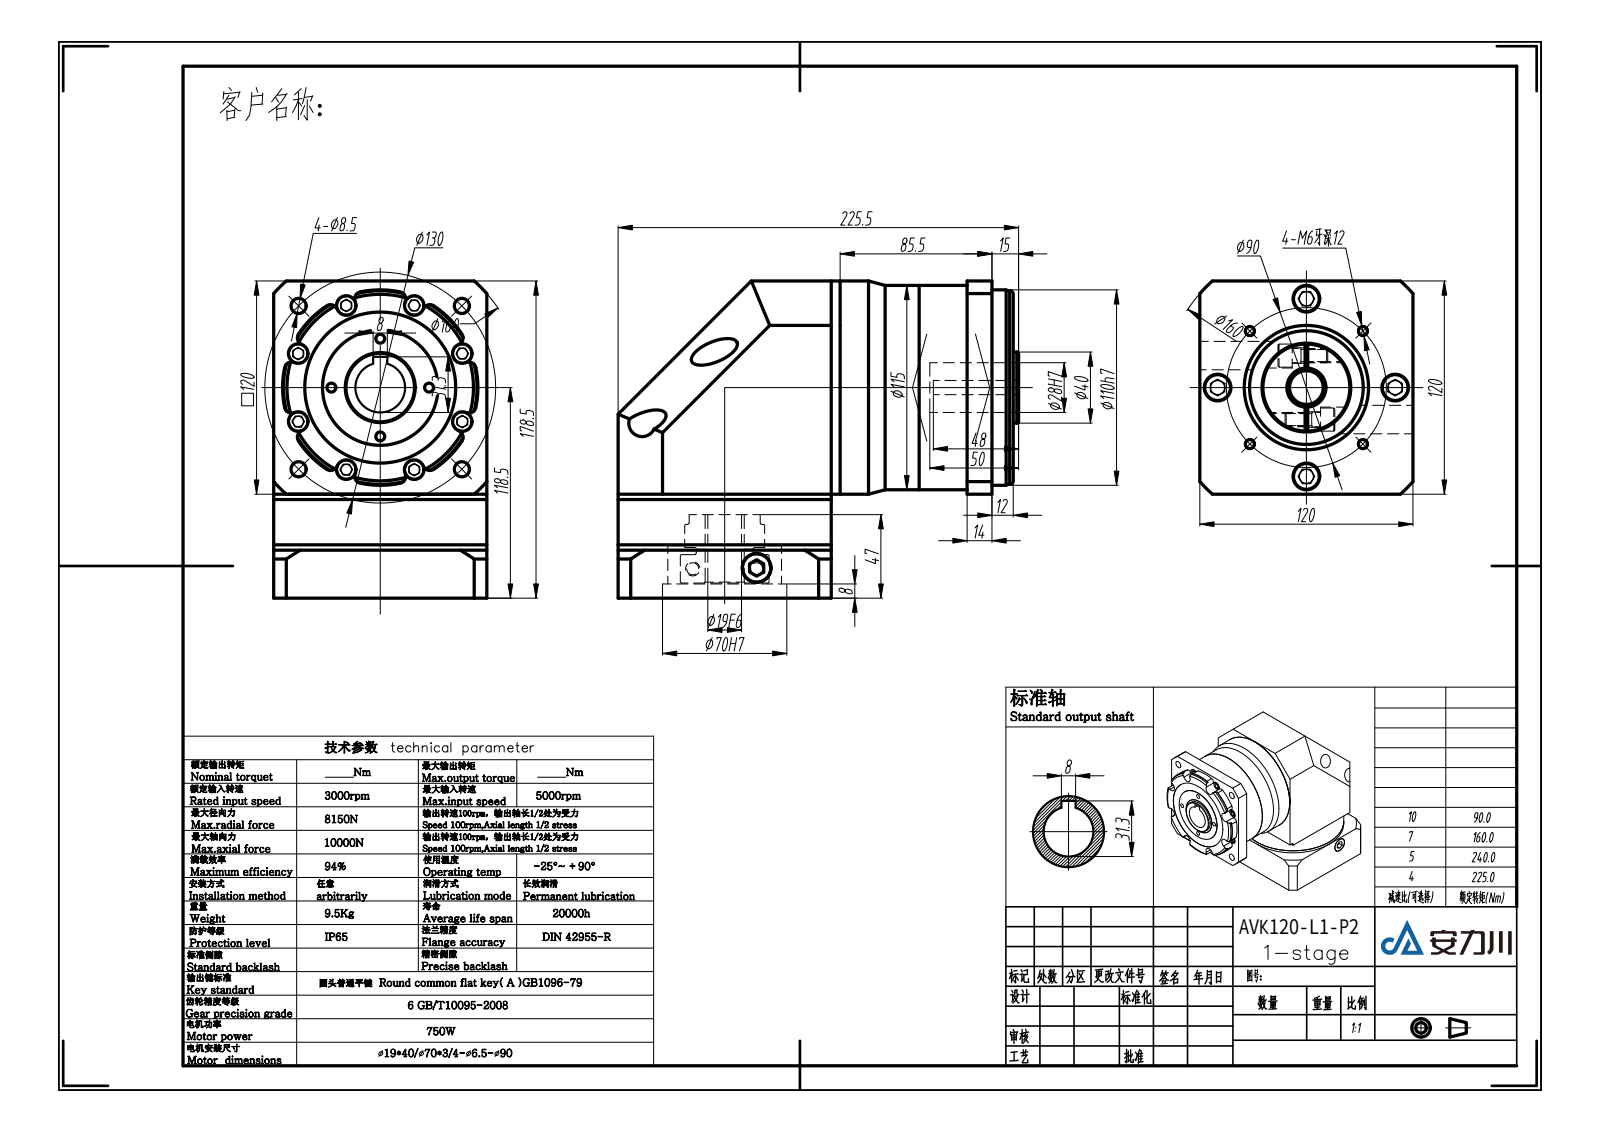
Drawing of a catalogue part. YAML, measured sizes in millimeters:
part_name: "VGZK115单级模型（19-40 70-3 4-6.5-90）"
step_written_by: "SolidWorks 2016 (AUTOMOTIVE_DESIGN)"
units: millimeters
bodies: {solids: 23, faces: 501, planar: 278, cylindrical: 198, other: 25}
overall_size: [225.5, 178.5, 120]
volume: 2959000
surface_area: 332399
round_holes:
  - {diameter: 15, count: 10}
  - {diameter: 5, count: 8}
  - {diameter: 11, count: 8}
  - {diameter: 8.5, count: 4}
  - {diameter: 16, count: 2}
  - {diameter: 19, count: 1}
  - {diameter: 20, count: 1}
  - {diameter: 22, count: 1}
  - {diameter: 28, count: 1}
  - {diameter: 45.2, count: 1}
  - {diameter: 70, count: 1}
  - {diameter: 85, count: 1}
round_bosses_or_shafts:
  - {diameter: 13, count: 10}
  - {diameter: 9.5, count: 8}
  - {diameter: 120, count: 2}
  - {diameter: 15.6, count: 2}
  - {diameter: 115, count: 1}
  - {diameter: 65, count: 1}
  - {diameter: 50, count: 1}
  - {diameter: 45, count: 1}
partial_cylinders:
  - {radius: 4, count: 16}
  - {radius: 80, count: 2}
  - {radius: 54.5, count: 1}
  - {radius: 55, count: 1}
face_to_face_distances: [5, 25.5, 120, 49.5, 44.5, 19.17, 25.33, 30.33, 55.5, 30]
hole_center_spacings: [39.29, 94.69, 26.74, 26.83, 36.65, 46.94, 49.53, 49.99]
